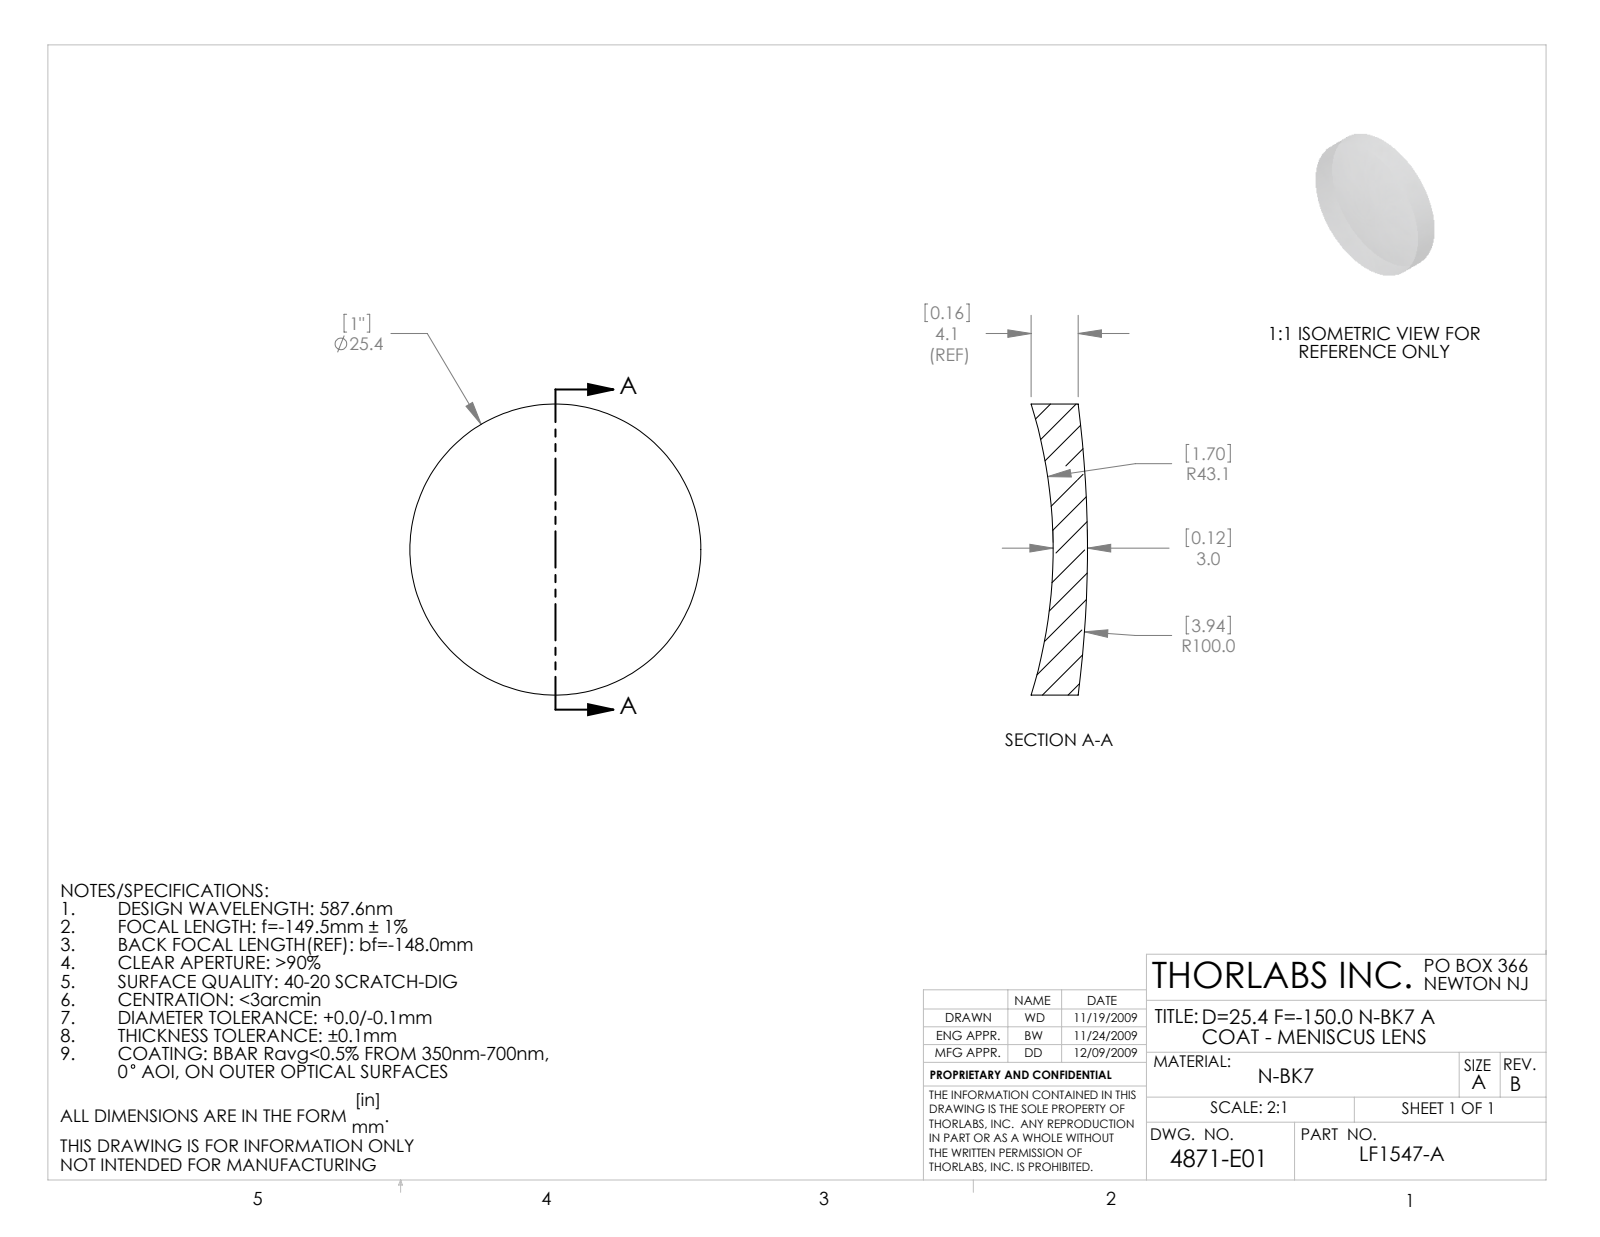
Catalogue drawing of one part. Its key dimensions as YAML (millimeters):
part_name: "4871-E0W"
step_written_by: "SolidWorks 2009 (AUTOMOTIVE_DESIGN)"
units: millimeters
bodies: {solids: 1, faces: 6, planar: 0, cylindrical: 2, other: 4}
overall_size: [25.4, 25.4, 4.91]
volume: 1796
surface_area: 1354
round_bosses_or_shafts:
  - {diameter: 25.4, count: 1}
